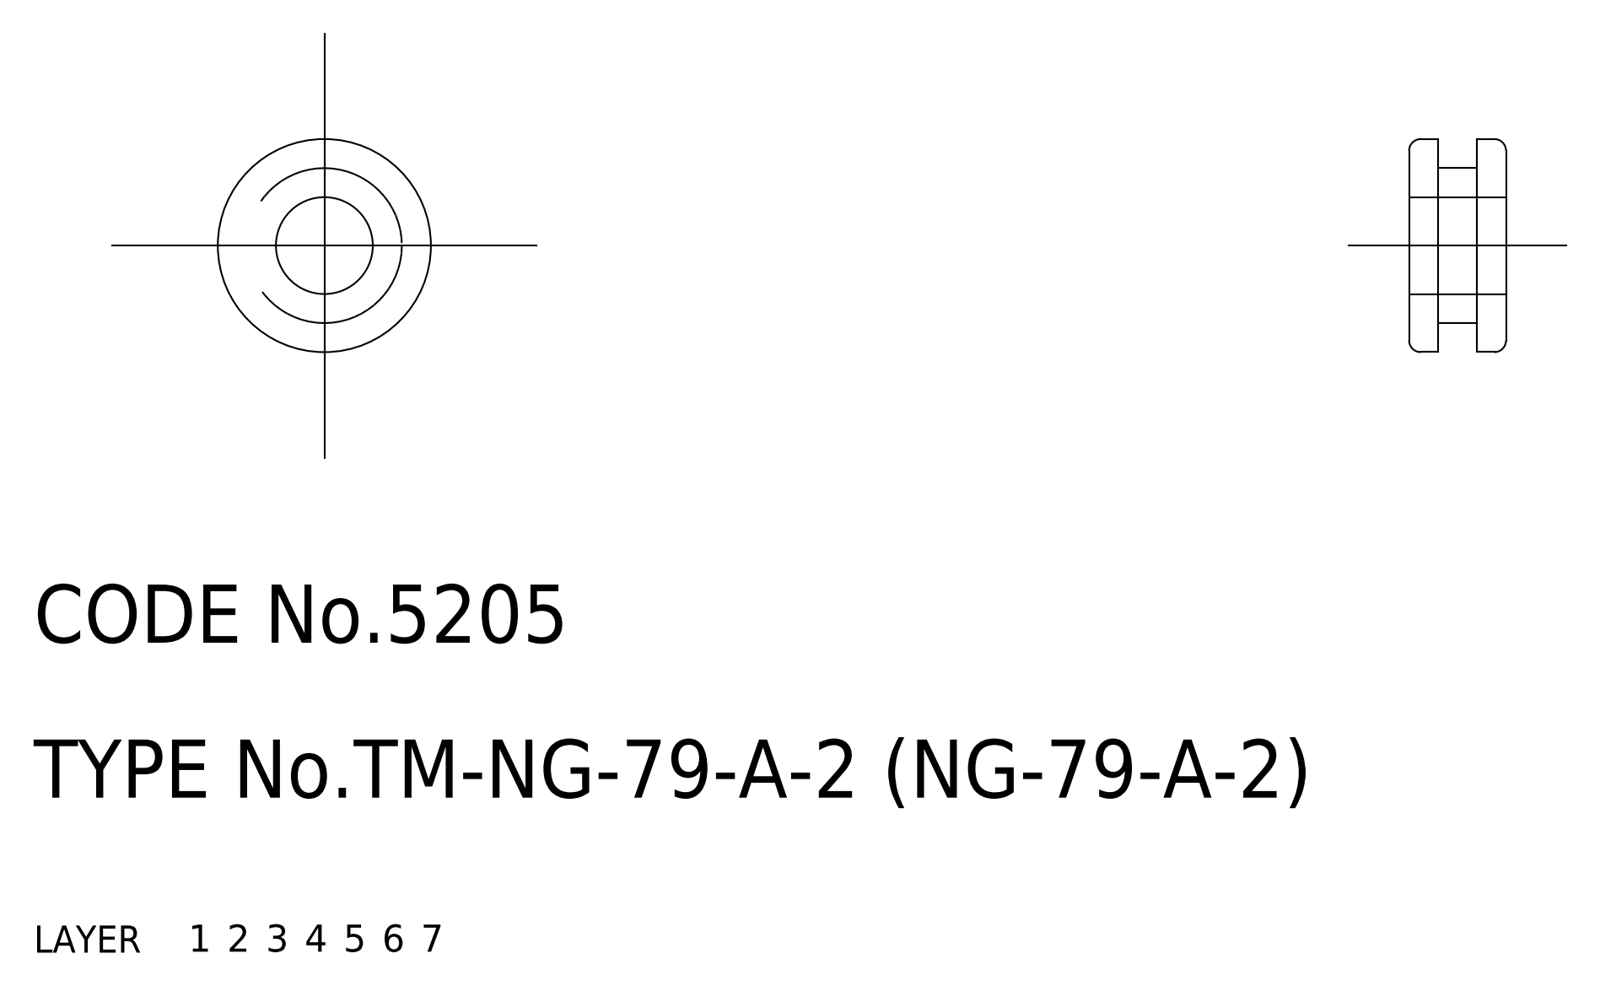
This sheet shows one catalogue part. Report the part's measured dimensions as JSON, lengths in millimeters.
{"part_name": "grommet", "step_written_by": "CADfix (AUTOMOTIVE_DESIGN)", "units": "millimeters", "bodies": {"solids": 1, "faces": 16, "planar": 0, "cylindrical": 0, "other": 16}, "overall_size": [11, 11, 5], "volume_mm3": 283, "surface_area_mm2": 455}
